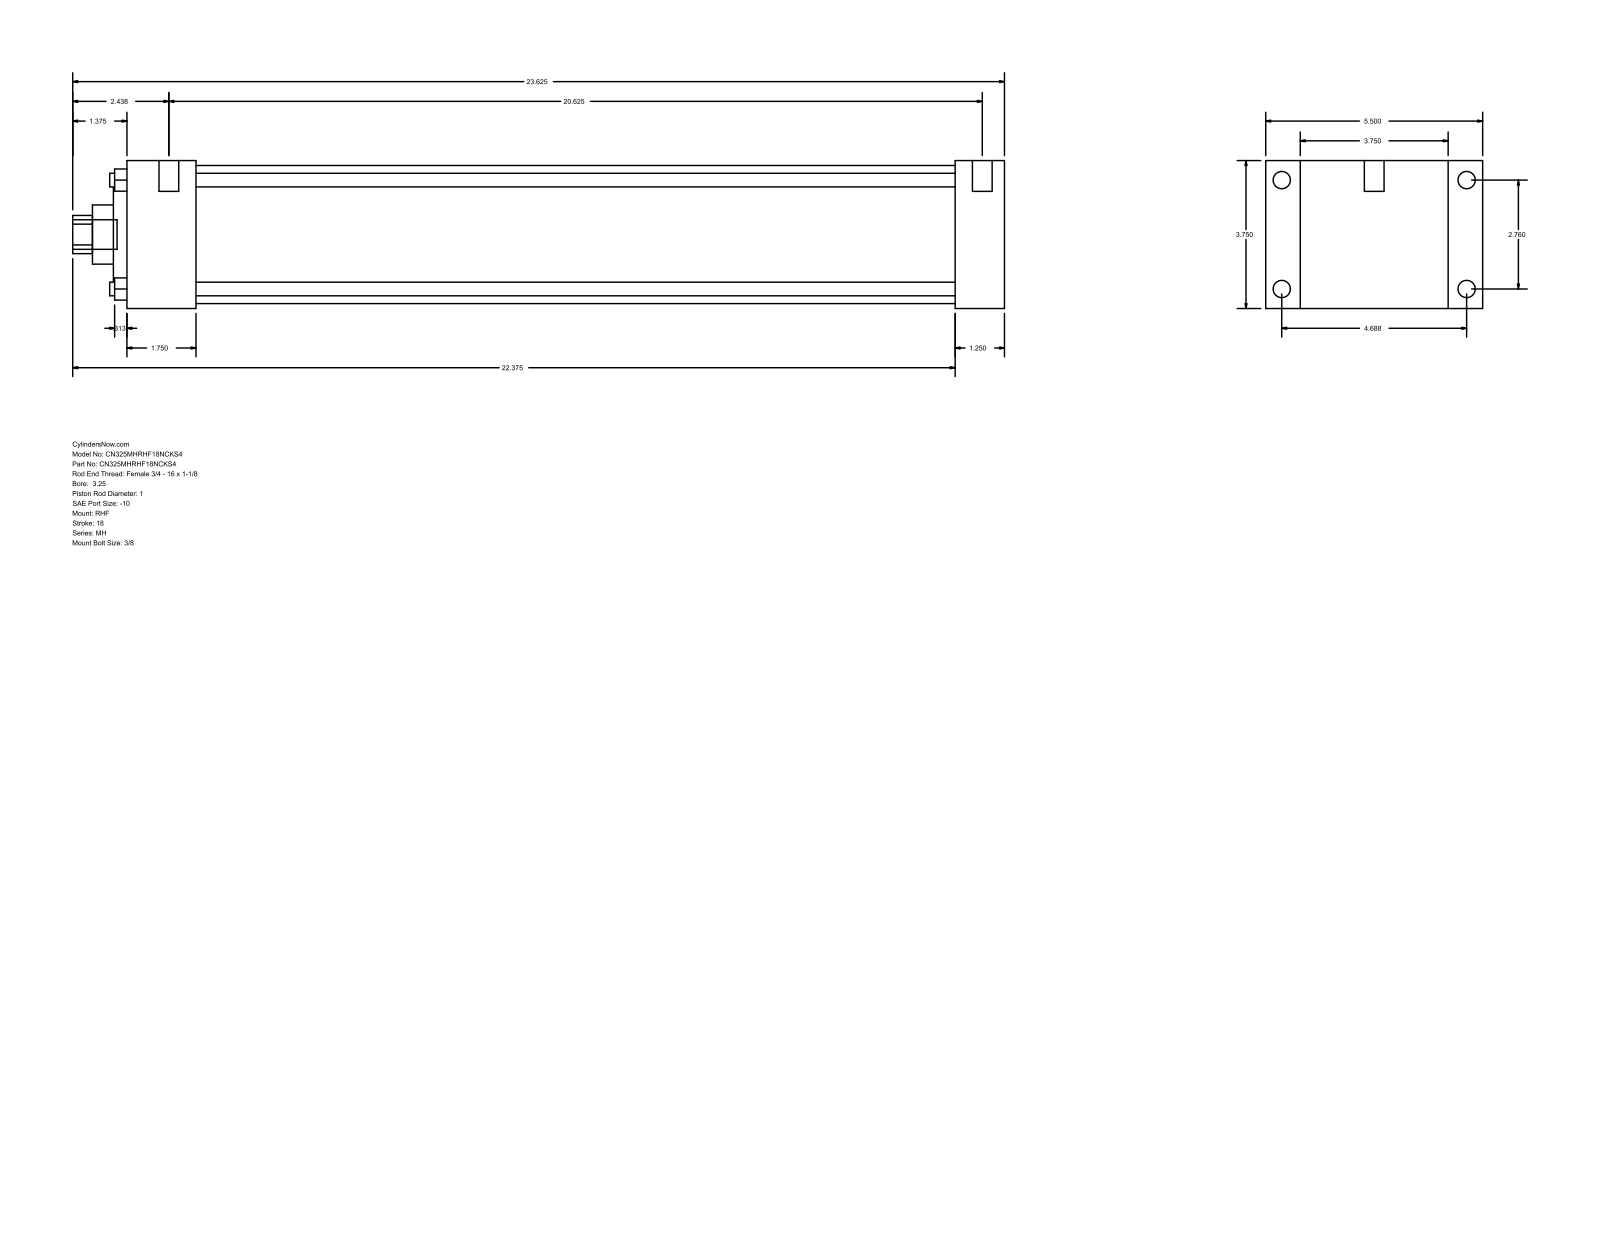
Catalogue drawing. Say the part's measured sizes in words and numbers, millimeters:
The part is named "MH_RHF__0325_1". Its 3-D file was written by "GSSL Pune (CONFIG_CONTROL_DESIGN)". It is 0 solids with 90 faces: 61 planar, 29 cylindrical and 0 other. Overall it measures 600.08 by 139.7 by 95.25 millimeters. Round holes: 4 of diameter 8.76, 1 of diameter 25.4, 1 of diameter 38.1, 1 of diameter 60.33, 1 of diameter 88.9. Round bosses or shafts: 4 of diameter 11.13, 4 of diameter 5.56, 2 of diameter 12.7, 1 of diameter 19.05. Partial cylindrical surfaces (rounded edges, fillets, slot ends): 1 of radius 12.29. The main face-to-face distances are 95.24, 31.75, 22.23, 117.47, 533.41, 565.16, 139.7, 44.46, 488.95, 520.7. The hole center spacings are 49.57, 70.1, 99.14.
